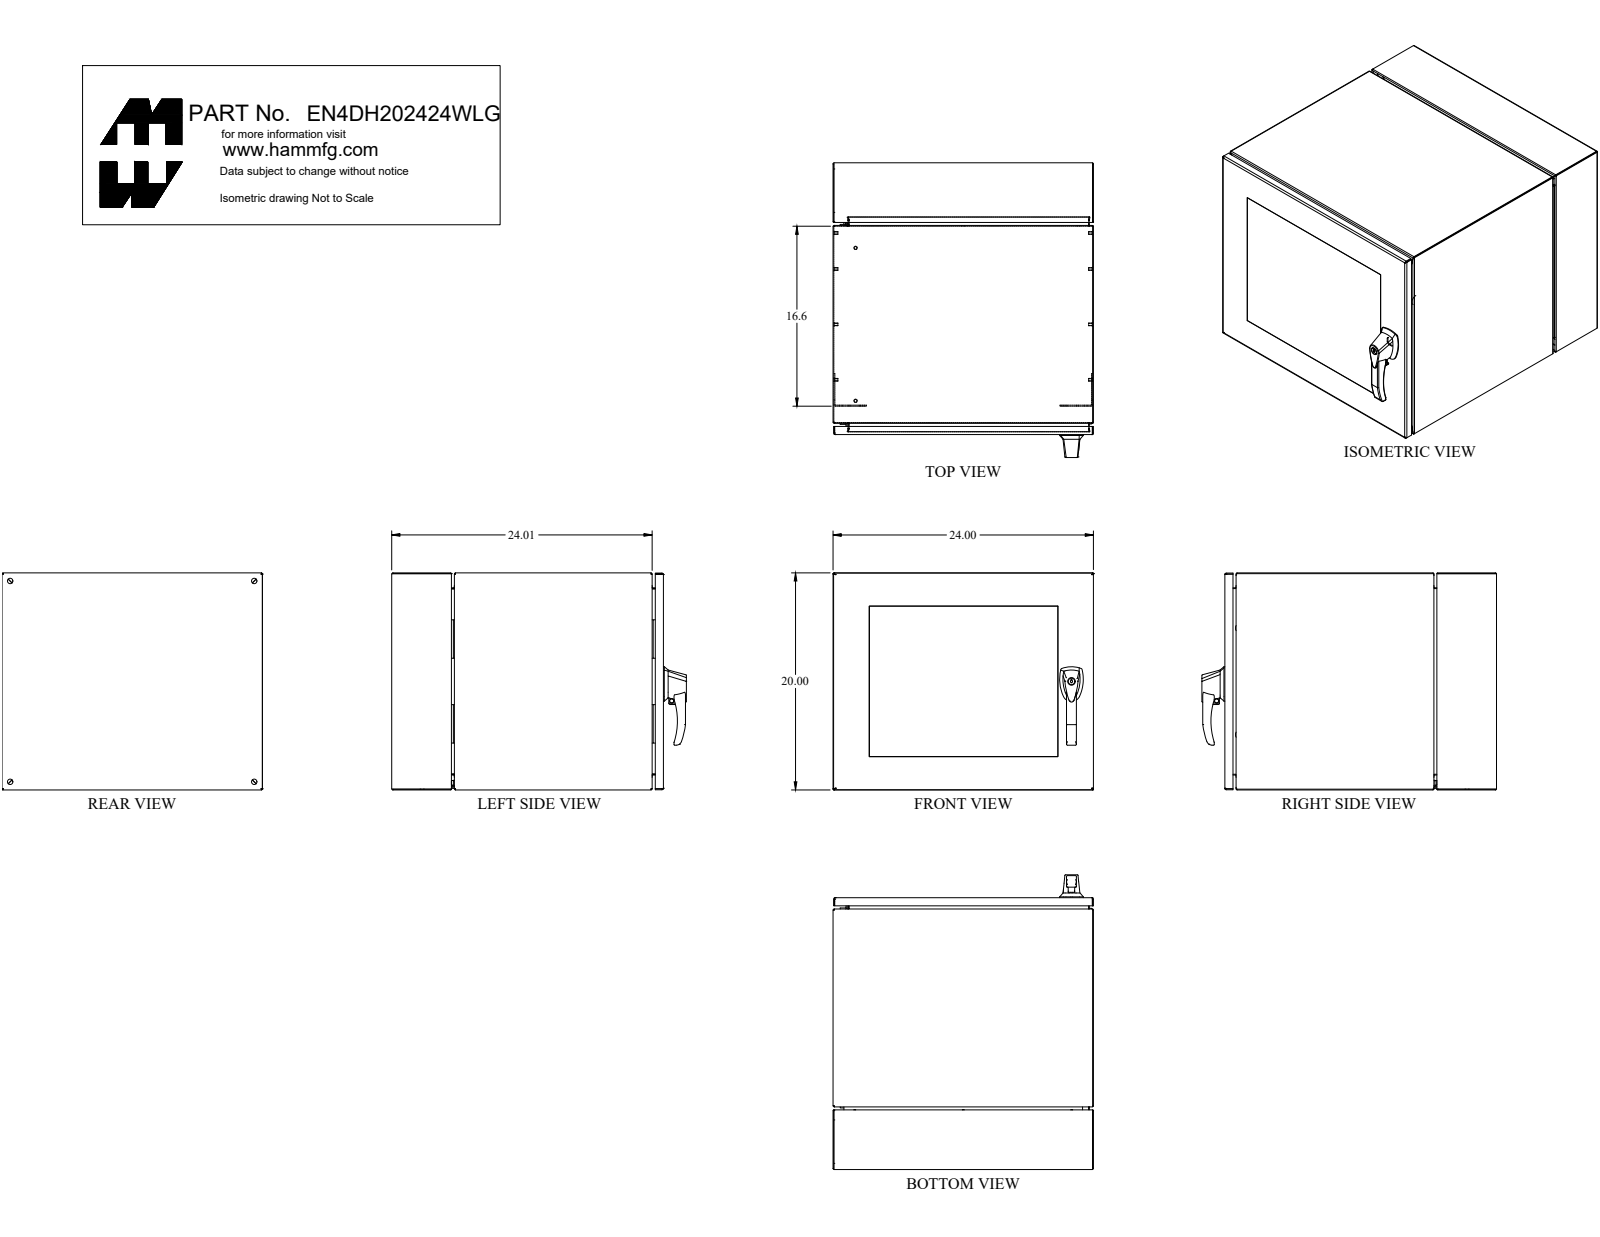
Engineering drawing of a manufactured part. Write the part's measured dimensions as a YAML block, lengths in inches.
part_name: "EN4DH202424WLG"
step_written_by: "SolidWorks 2019 (CONFIG_CONTROL_DESIGN)"
units: inches
bodies: {solids: 214, faces: 4002, planar: 2229, cylindrical: 983, other: 790}
overall_size: [27.158, 24.001, 20]
volume: 390.2
surface_area: 8698
round_holes:
  - {diameter: 0.177, count: 60}
  - {diameter: 0.25, count: 31}
  - {diameter: 0.125, count: 18}
  - {diameter: 0.13, count: 18}
  - {diameter: 0.196, count: 15}
  - {diameter: 0.188, count: 8}
  - {diameter: 0.194, count: 8}
  - {diameter: 0.237, count: 8}
  - {diameter: 0.257, count: 7}
  - {diameter: 0.275, count: 7}
  - {diameter: 0.281, count: 7}
  - {diameter: 0.173, count: 6}
round_bosses_or_shafts:
  - {diameter: 0.25, count: 24}
  - {diameter: 0.313, count: 22}
  - {diameter: 0.368, count: 18}
  - {diameter: 0.226, count: 16}
  - {diameter: 0.164, count: 16}
  - {diameter: 0.236, count: 10}
  - {diameter: 0.625, count: 9}
  - {diameter: 0.472, count: 8}
partial_cylinders:
  - {radius: 0.036, count: 34}
  - {radius: 0.108, count: 34}
  - {radius: 0.125, count: 29}
  - {radius: 0.25, count: 18}
  - {radius: 0.06, count: 16}
  - {radius: 0.048, count: 13}
  - {radius: 0.143, count: 13}
  - {radius: 0.079, count: 12}
face_to_face_distances: [0.072, 19.928, 23.928, 0.095, 19.856, 20, 23.856, 24.971, 25.043, 24]
hole_center_spacings: [3.5, 7, 2.25, 1.25, 10.5, 1.125, 1.125, 2.375]
